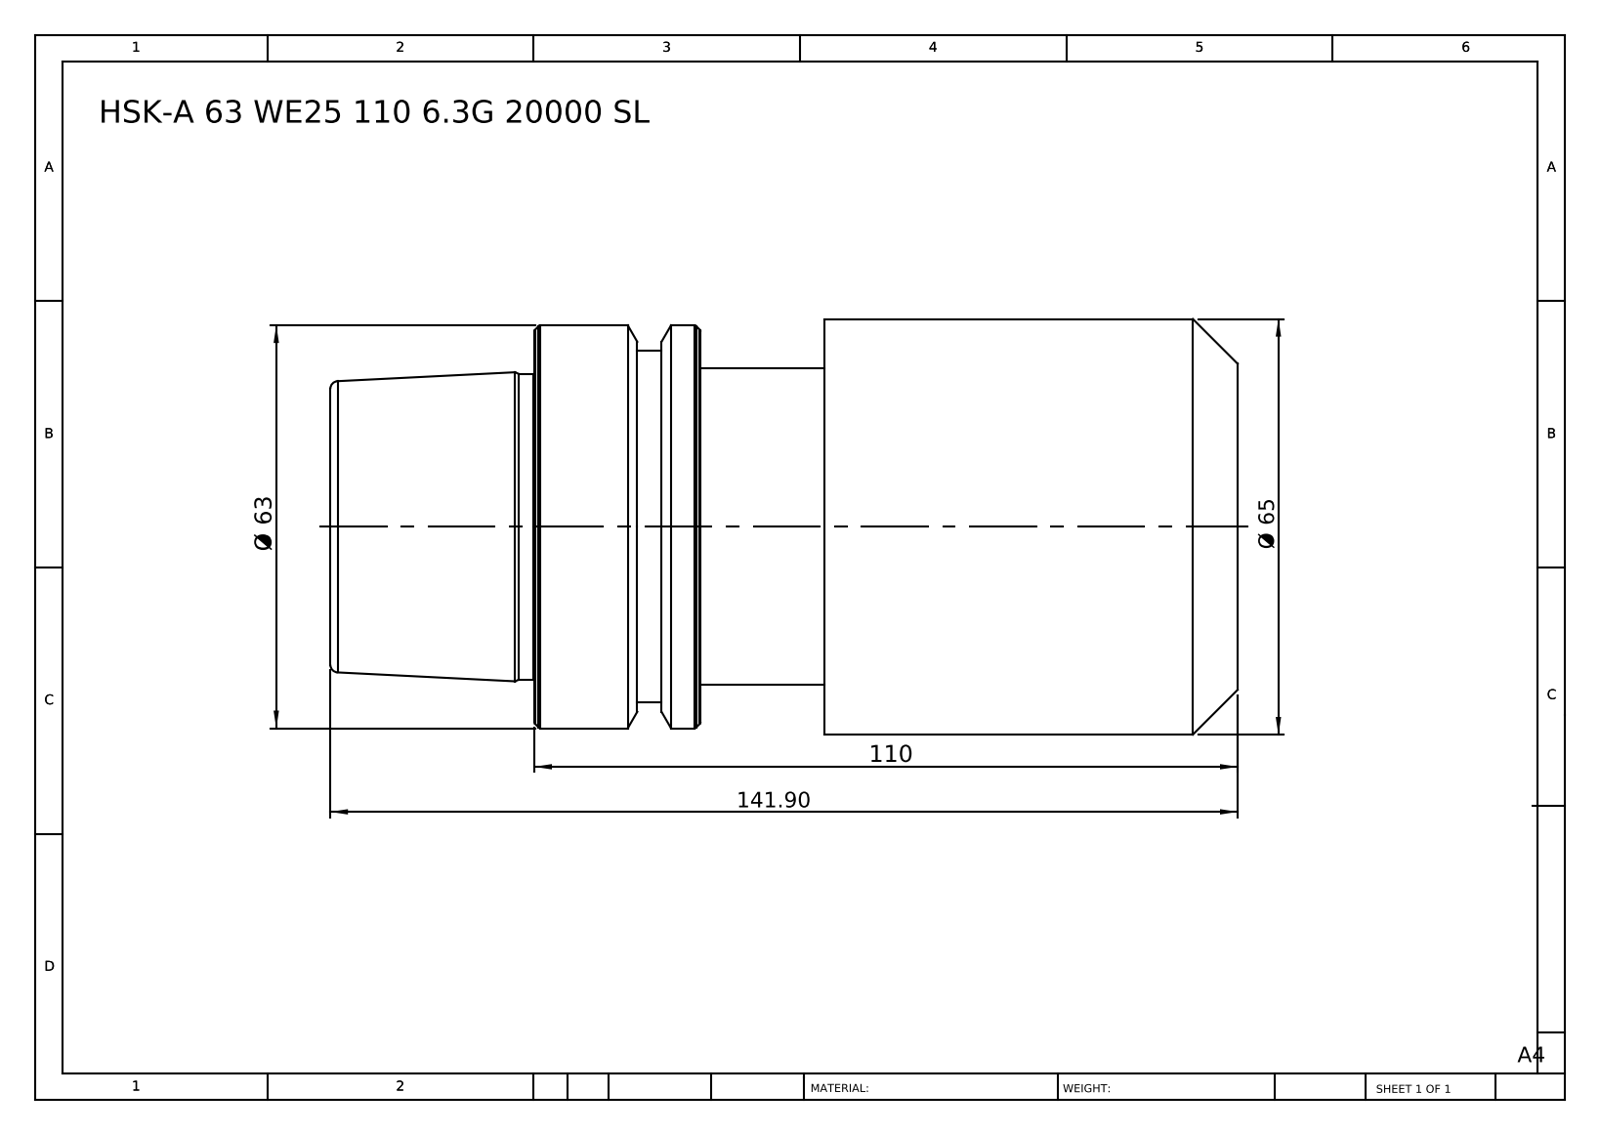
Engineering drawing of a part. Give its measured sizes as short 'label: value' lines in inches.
name: HSK-A 63 WE25 110 6.3G 20000 SL
written by: SolidWorks 2014 (CONFIG_CONTROL_DESIGN)
unit: in
bodies: 1 solid, 47 faces (7 planar, 12 cylindrical, 28 other)
size: 5.587 × 2.559 × 2.559
volume: 23.17 in³; area: 53.85 in²
bosses: 1× ⌀2.559, 1× ⌀2.48, 1× ⌀2.165, 1× ⌀1.949, 1× ⌀1.881
face distances: 5.587, 2.544, 3.043, 3.307, 0.763, 2.28, 4.331, 1.787, 1.024, 1.256
